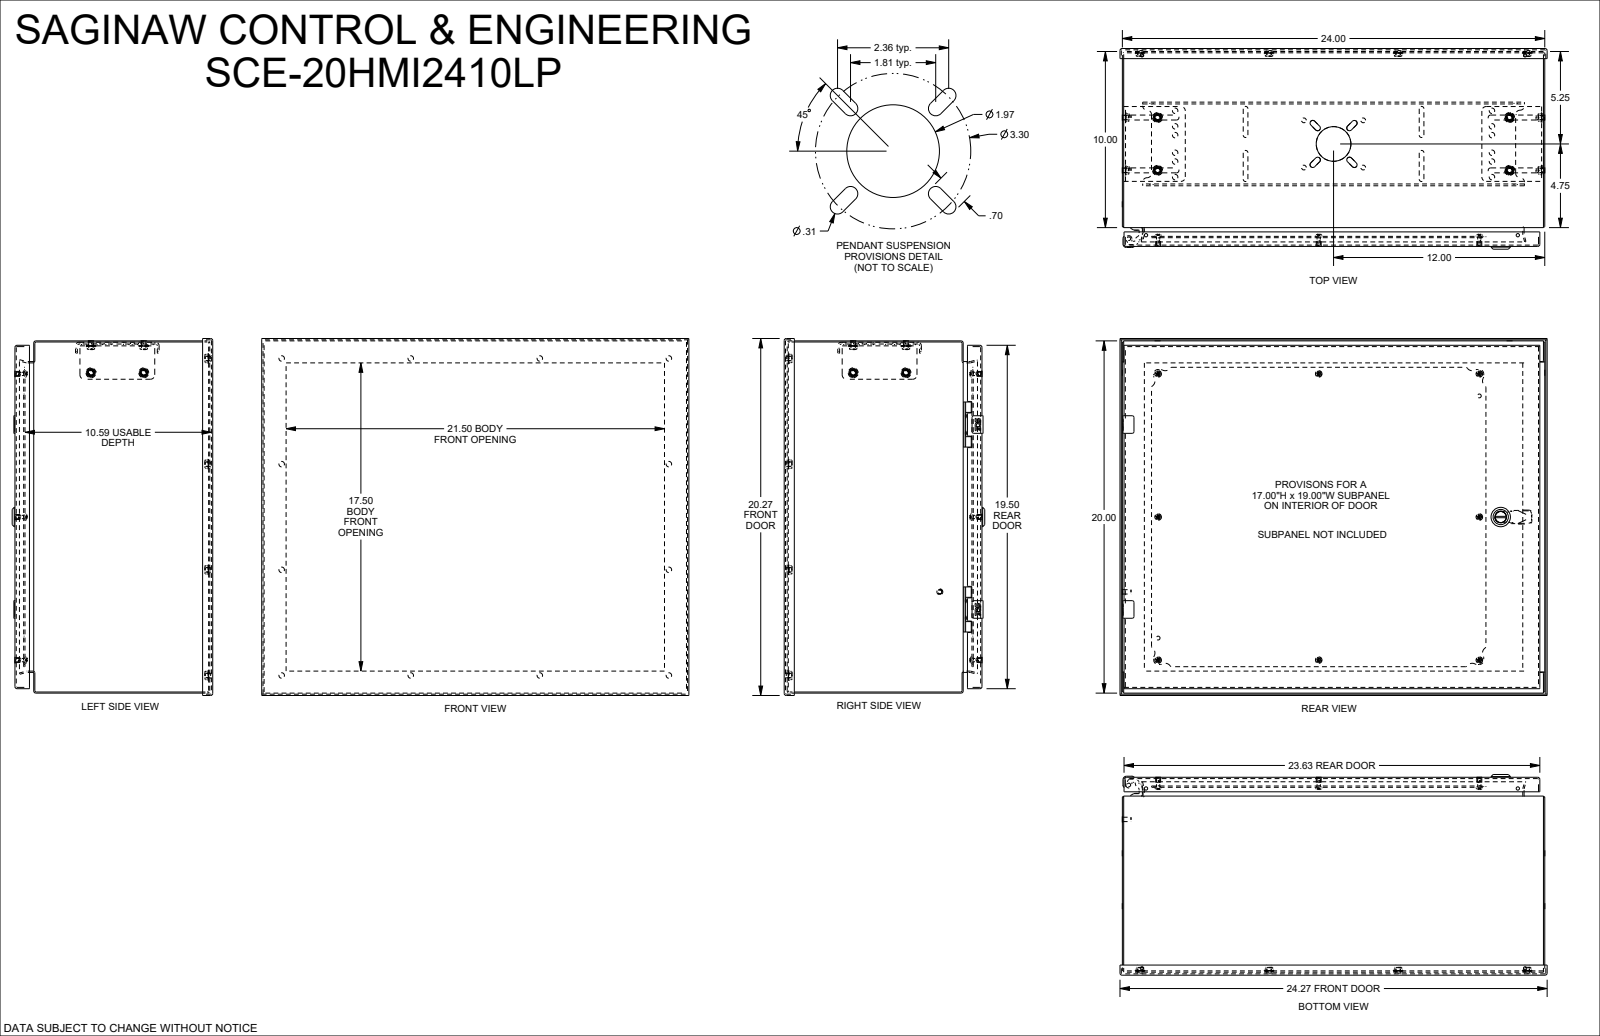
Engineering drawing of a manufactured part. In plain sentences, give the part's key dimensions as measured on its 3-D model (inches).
The part is named "SCE-20HMI2410LP". Its 3-D file was written by "SolidWorks 2023 (AUTOMOTIVE_DESIGN)". It is 24 solids with 2269 faces: 1110 planar, 714 cylindrical and 445 other. Overall it measures 24.27 by 20.27 by 11.395 inches. Its volume is 213.6 cubic inches and its surface area 5 394 square inches. Round holes: 12 of diameter 0.31, 12 of diameter 0.313, 8 of diameter 0.19, 8 of diameter 0.25, 7 of diameter 0.25, 4 of diameter 0.172, 4 of diameter 0.205, 4 of diameter 0.218, 4 of diameter 0.244, 4 of diameter 0.266, 4 of diameter 0.27, 4 of diameter 0.281. Round bosses or shafts: 19 of diameter 0.248, 8 of diameter 0.373, 8 of diameter 0.28, 8 of diameter 0.188, 7 of diameter 0.337, 6 of diameter 0.17, 4 of diameter 0.25, 4 of diameter 0.24. Partial cylindrical surfaces (rounded edges, fillets, slot ends): 30 of radius 0.012, 28 of radius 0.25, 24 of radius 0.015, 16 of radius 0.22, 13 of radius 0.06, 12 of radius 0.02, 12 of radius 0.1, 12 of radius 0.141. The main face-to-face distances are 0.075, 10.667, 0.075, 0.06, 11.163, 11.103, 11.178, 11.238, 0.496, 0.436. The hole center spacings are 18, 6, 22.804, 0.494, 0.5, 0.883, 1.071, 1.118.
